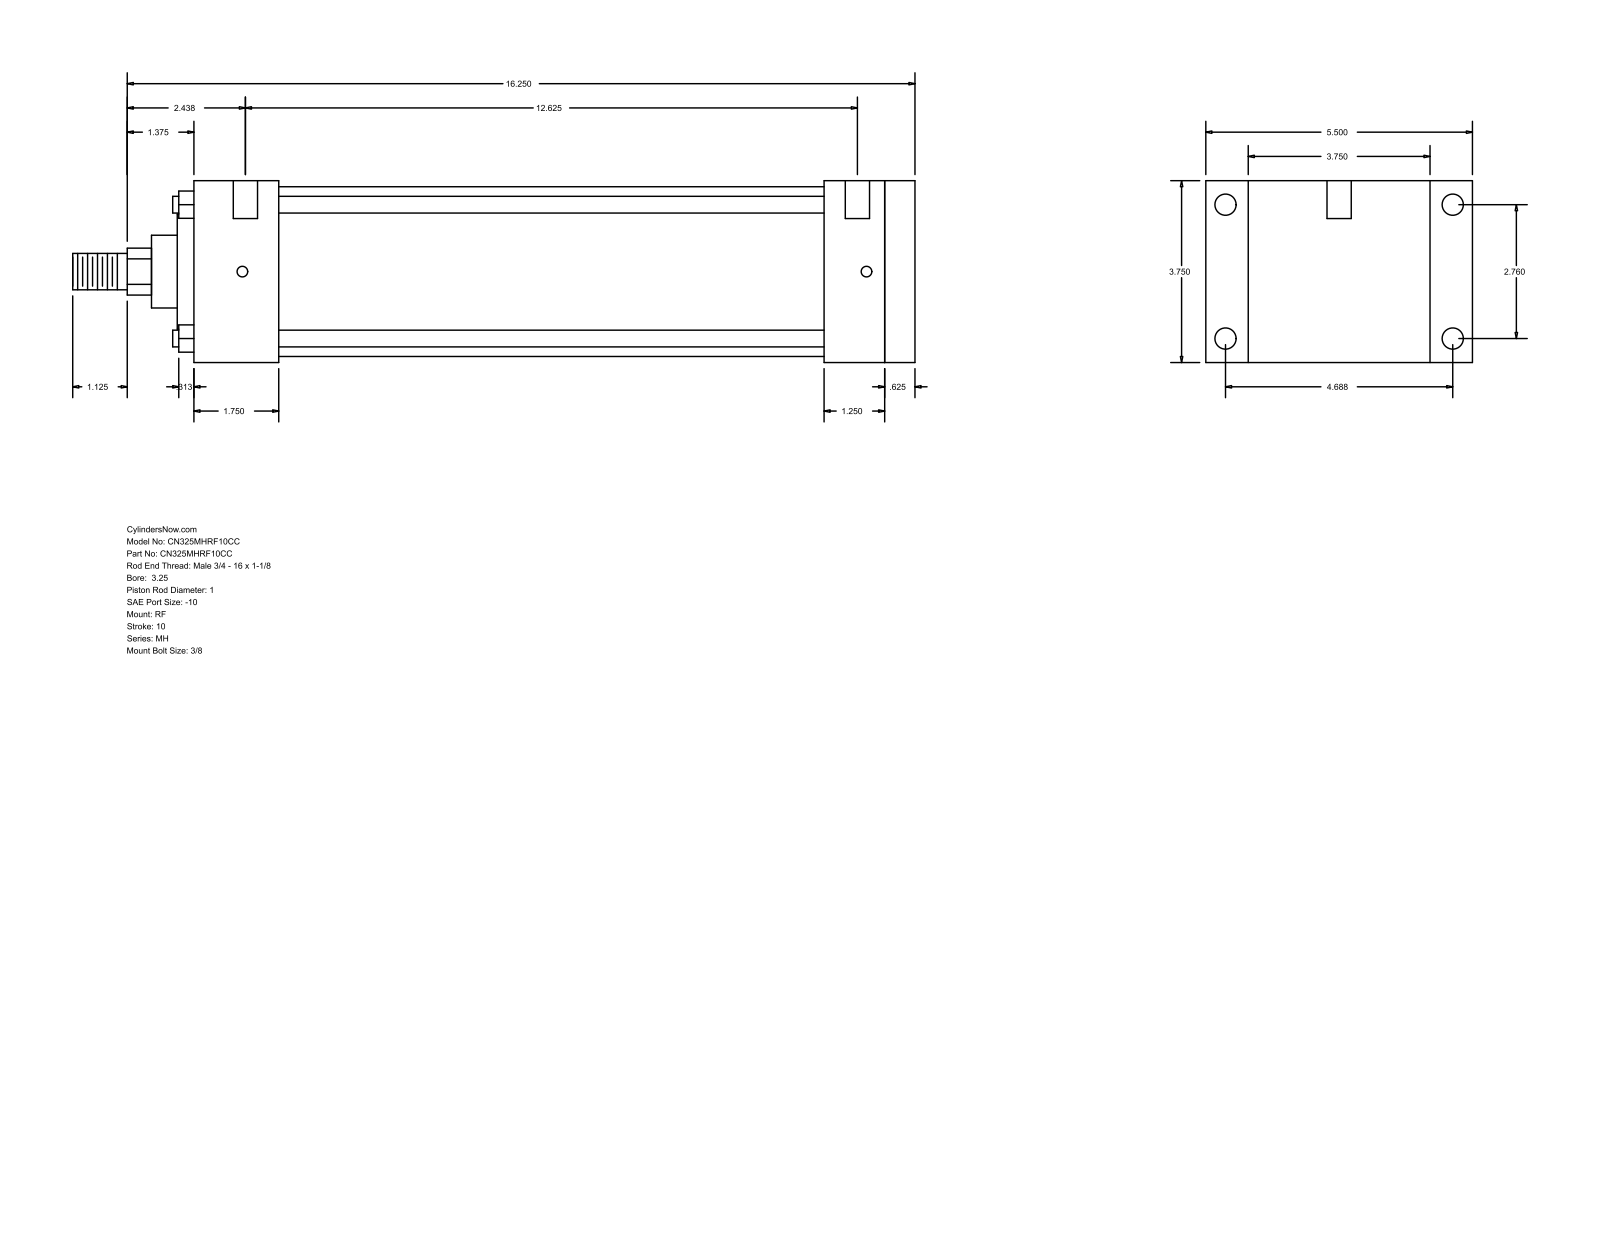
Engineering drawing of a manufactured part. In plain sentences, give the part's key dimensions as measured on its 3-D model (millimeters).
The part is named "MH_RF__0325_1". Its 3-D file was written by "GSSL Pune (CONFIG_CONTROL_DESIGN)". It is 0 solids with 94 faces: 65 planar, 29 cylindrical and 0 other. Overall it measures 441.32 by 139.7 by 95.25 millimeters. Round holes: 4 of diameter 5.56, 4 of diameter 11.13, 2 of diameter 12.7. Round bosses or shafts: 4 of diameter 8.76, 1 of diameter 88.9, 1 of diameter 60.33, 1 of diameter 38.1, 1 of diameter 25.4, 1 of diameter 19.05. Partial cylindrical surfaces (rounded edges, fillets, slot ends): 1 of radius 12.29. The main face-to-face distances are 95.24, 377.83, 361.96, 15.87, 22.23, 117.47, 44.46, 317.5, 333.37, 330.2. The hole center spacings are 70.1, 119.06, 138.16, 327.02, 1.58, 4.76, 320.68, 322.26.
